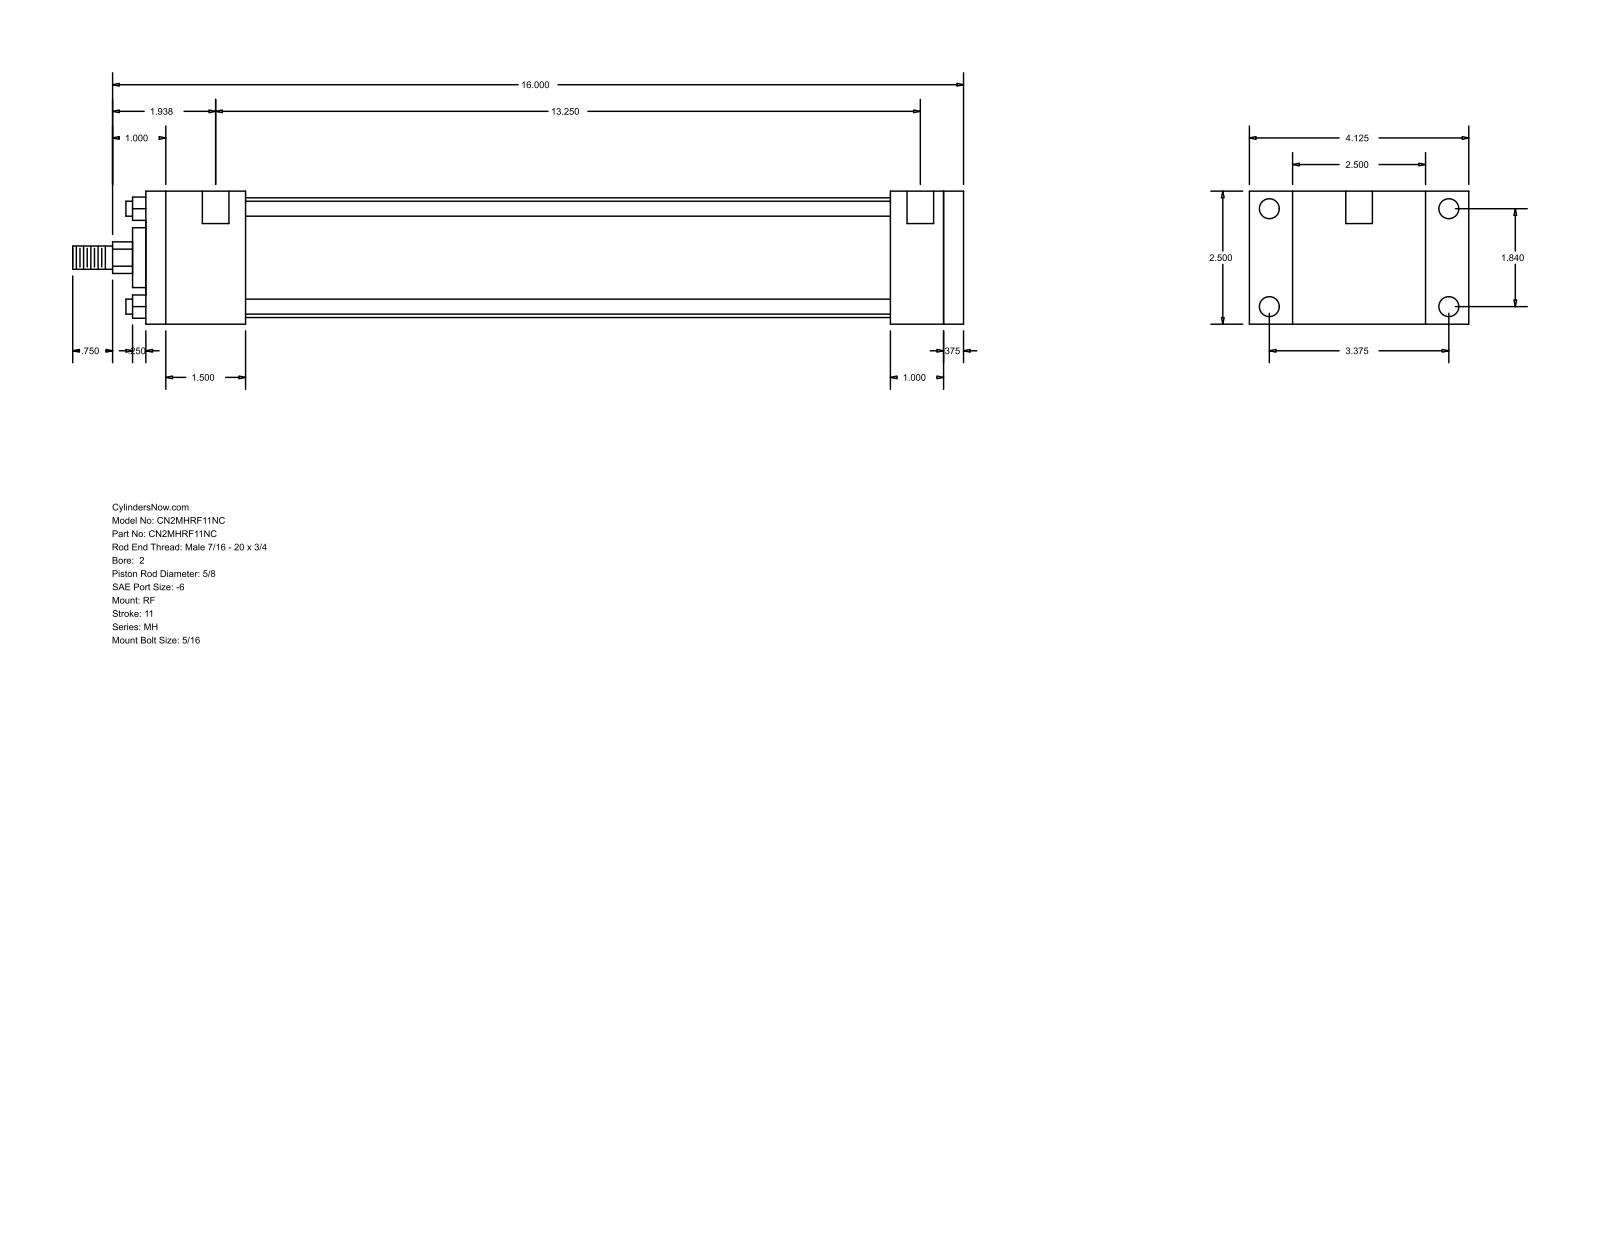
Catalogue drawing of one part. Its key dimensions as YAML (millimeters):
part_name: "MH_RF__0200_0.625"
step_written_by: "GSSL Pune (CONFIG_CONTROL_DESIGN)"
units: millimeters
bodies: {solids: 0, faces: 92, planar: 64, cylindrical: 28, other: 0}
overall_size: [425.45, 104.78, 63.5]
round_holes:
  - {diameter: 5.56, count: 4}
  - {diameter: 9.53, count: 4}
  - {diameter: 12.7, count: 2}
round_bosses_or_shafts:
  - {diameter: 7.14, count: 4}
  - {diameter: 57.15, count: 1}
  - {diameter: 28.57, count: 1}
  - {diameter: 15.88, count: 1}
  - {diameter: 11.11, count: 1}
partial_cylinders:
  - {radius: 7.54, count: 1}
face_to_face_distances: [63.5, 390.52, 381, 9.52, 25.4, 47.62, 355.6, 307.98, 333.38, 342.9]
hole_center_spacings: [46.74, 85.72, 97.63, 344.49, 3.18, 4.76, 336.55, 339.73]
